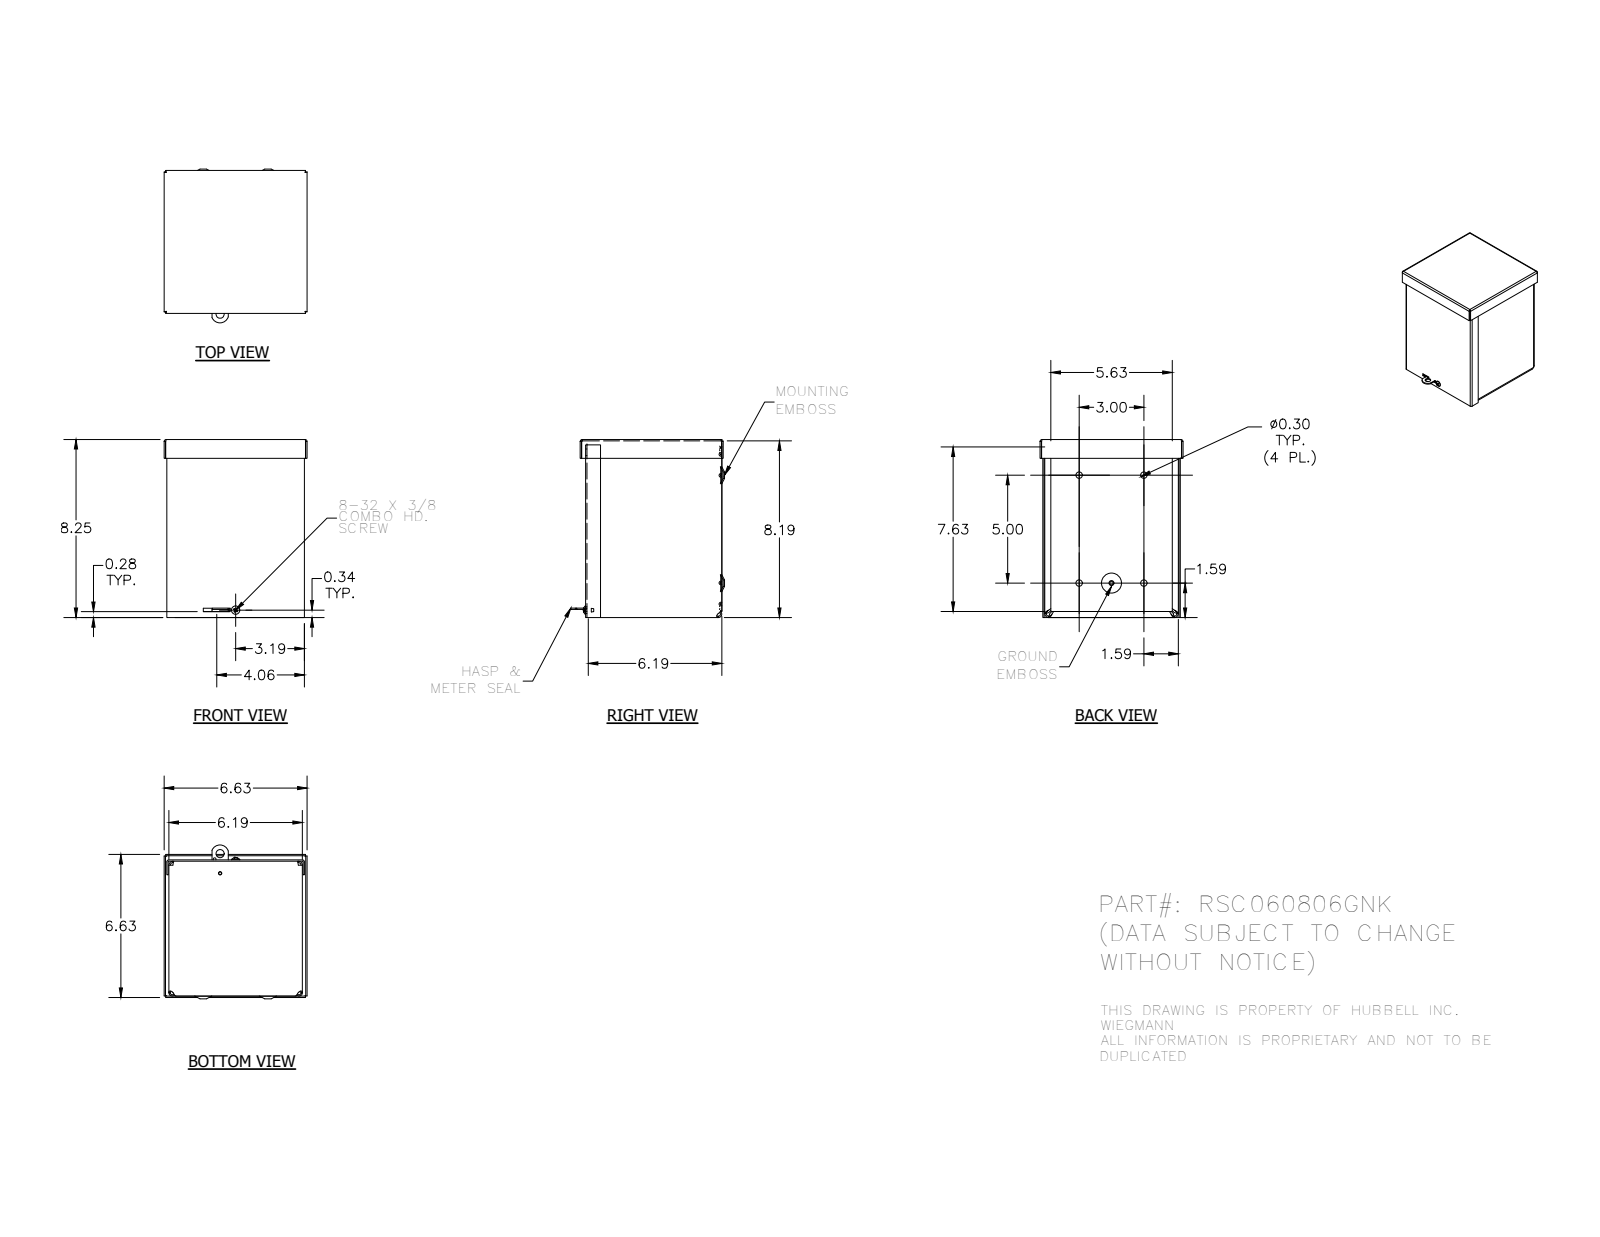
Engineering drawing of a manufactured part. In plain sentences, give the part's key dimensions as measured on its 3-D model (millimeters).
The part is named "RSC060806GNK_WRAP; RSC0608GNK_LID; RSC0606GNK_CAP; 3183 (+3 more)". Its 3-D file was written by "Autodesk Inventor 2014 (AUTOMOTIVE_DESIGN)". It is 6 solids with 347 faces: 153 planar, 73 cylindrical and 121 other. Overall it measures 209.56 by 180.97 by 168.28 millimeters. Its volume is 388 090 cubic millimeters and its surface area 500 379 square millimeters. Round holes: 4 of diameter 7.62, 2 of diameter 3.17, 2 of diameter 7.95, 1 of diameter 3.76, 1 of diameter 3.96, 1 of diameter 4.19, 1 of diameter 9.52. Round bosses or shafts: 1 of diameter 9.75, 1 of diameter 5.8, 1 of diameter 4.17. Partial cylindrical surfaces (rounded edges, fillets, slot ends): 8 of radius 0.79, 8 of radius 2.37, 8 of radius 3.17, 8 of radius 4.75, 4 of radius 1.4, 4 of radius 1.57, 4 of radius 2.38, 4 of radius 2.97. The main face-to-face distances are 1.58, 1.57, 155.59, 206.39, 158.73, 154.01, 157.17, 3.15, 157.15, 1.59. The hole center spacings are 38.1, 76.2, 127, 132.58, 148.11, 9.1, 17.84, 23.19.
